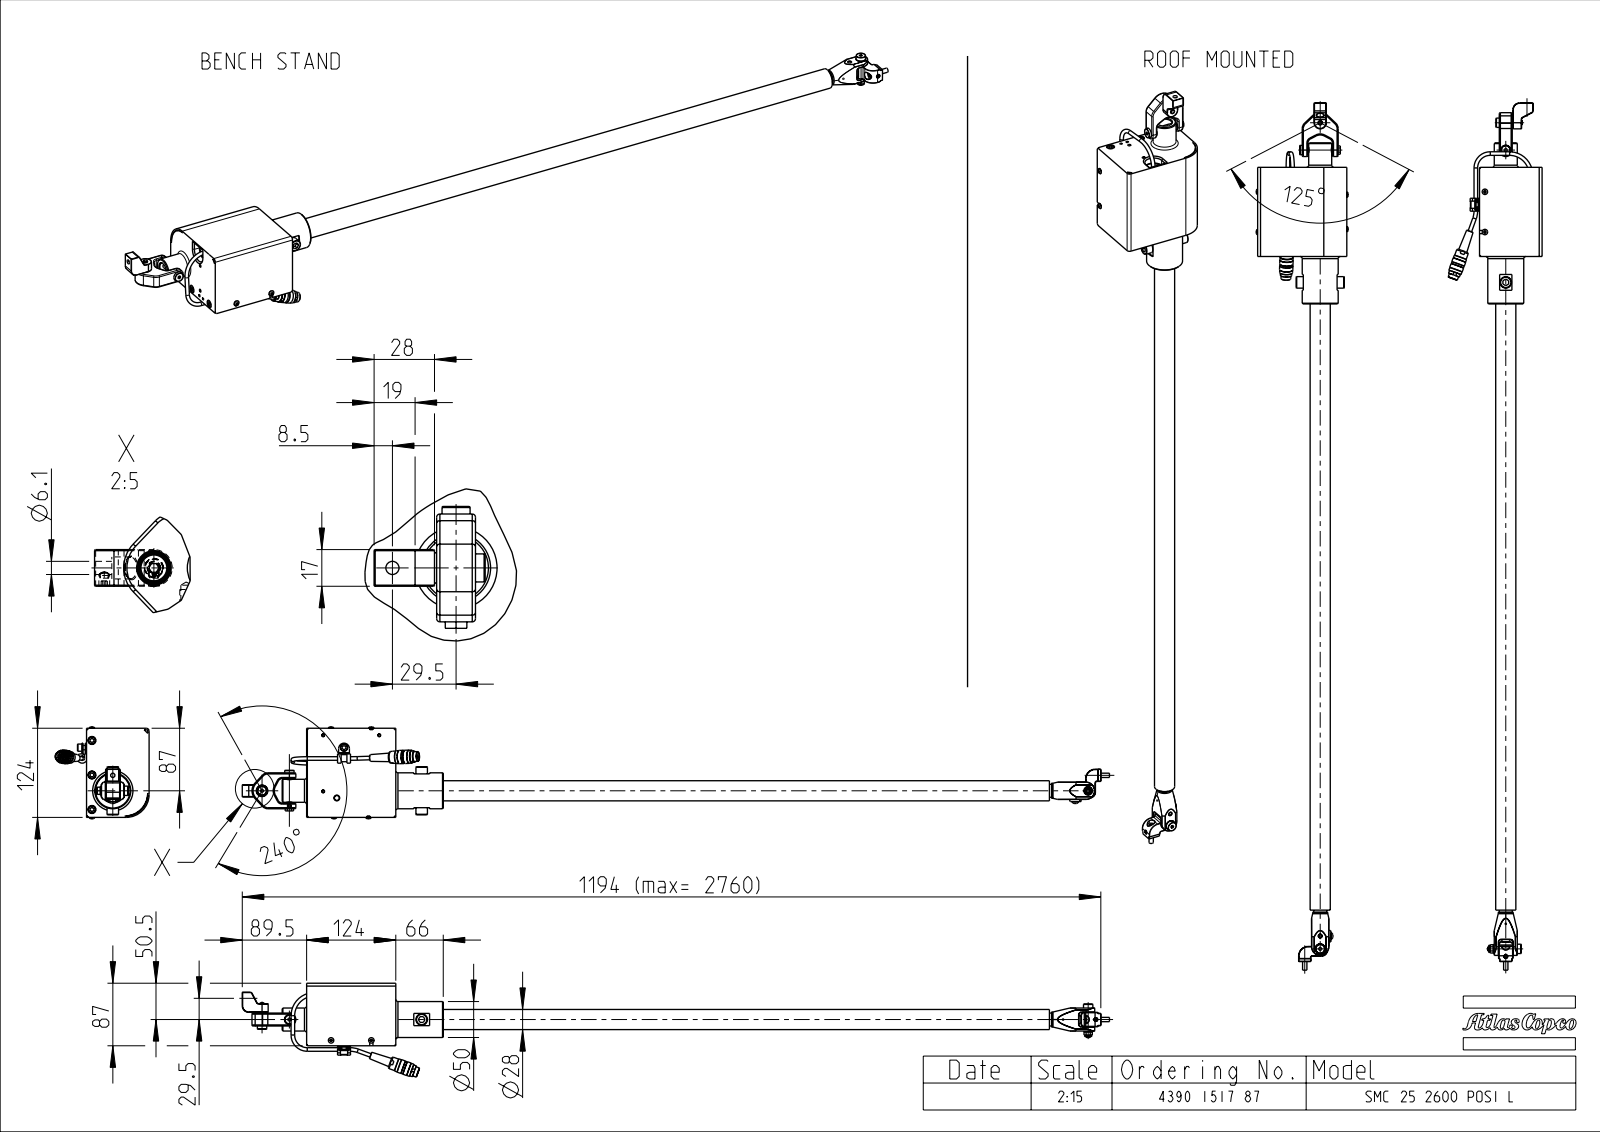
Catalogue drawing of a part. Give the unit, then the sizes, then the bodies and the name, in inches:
Units: inches
Overall size (bounding box): 47.48 × 5.141 × 5.039
Round holes (diameter × count): ⌀0.079 ×11, ⌀0.197 ×10, ⌀0.102 ×8, ⌀0.157 ×7, ⌀0.165 ×7, ⌀0.236 ×7, ⌀0.126 ×6, ⌀0.13 ×6, ⌀0.039 ×5, ⌀0.315 ×4, ⌀0.319 ×4, ⌀0.098 ×3
Round bosses / shafts (diameter × count): ⌀0.394 ×9, ⌀0.236 ×8, ⌀0.197 ×8, ⌀0.315 ×7, ⌀0.063 ×7, ⌀0.709 ×5, ⌀0.043 ×5, ⌀0.165 ×4
Partial cylindrical surfaces — rounded edges, fillets, slot ends (radius × count): R0.005 ×72, R0.01 ×48, R0.027 ×36, R0.02 ×26, R0.059 ×24, R0.004 ×15, R0.012 ×14, R0.276 ×7
Main face-to-face distances: 0.079, 0.472, 4.409, 4.882, 0.591, 2.835, 3.425, 4.803, 2.756, 3.346
Hole centre spacings: 0.945, 1.62, 0.098, 0.139, 1.637, 2.826, 0.079, 0.362
Volume: 14.76 in³ · Surface area: 1 008 in²
Bodies: 34 solids, 3274 faces (1605 planar, 1044 cylindrical, 625 other)
Part name (STEP PRODUCT): 4390151787
STEP written by: PRO/ENGINEER BY PARAMETRIC TECHNOLOGY CORPORATION, 2011410 (CONFIG_CONTROL_DESIGN)
